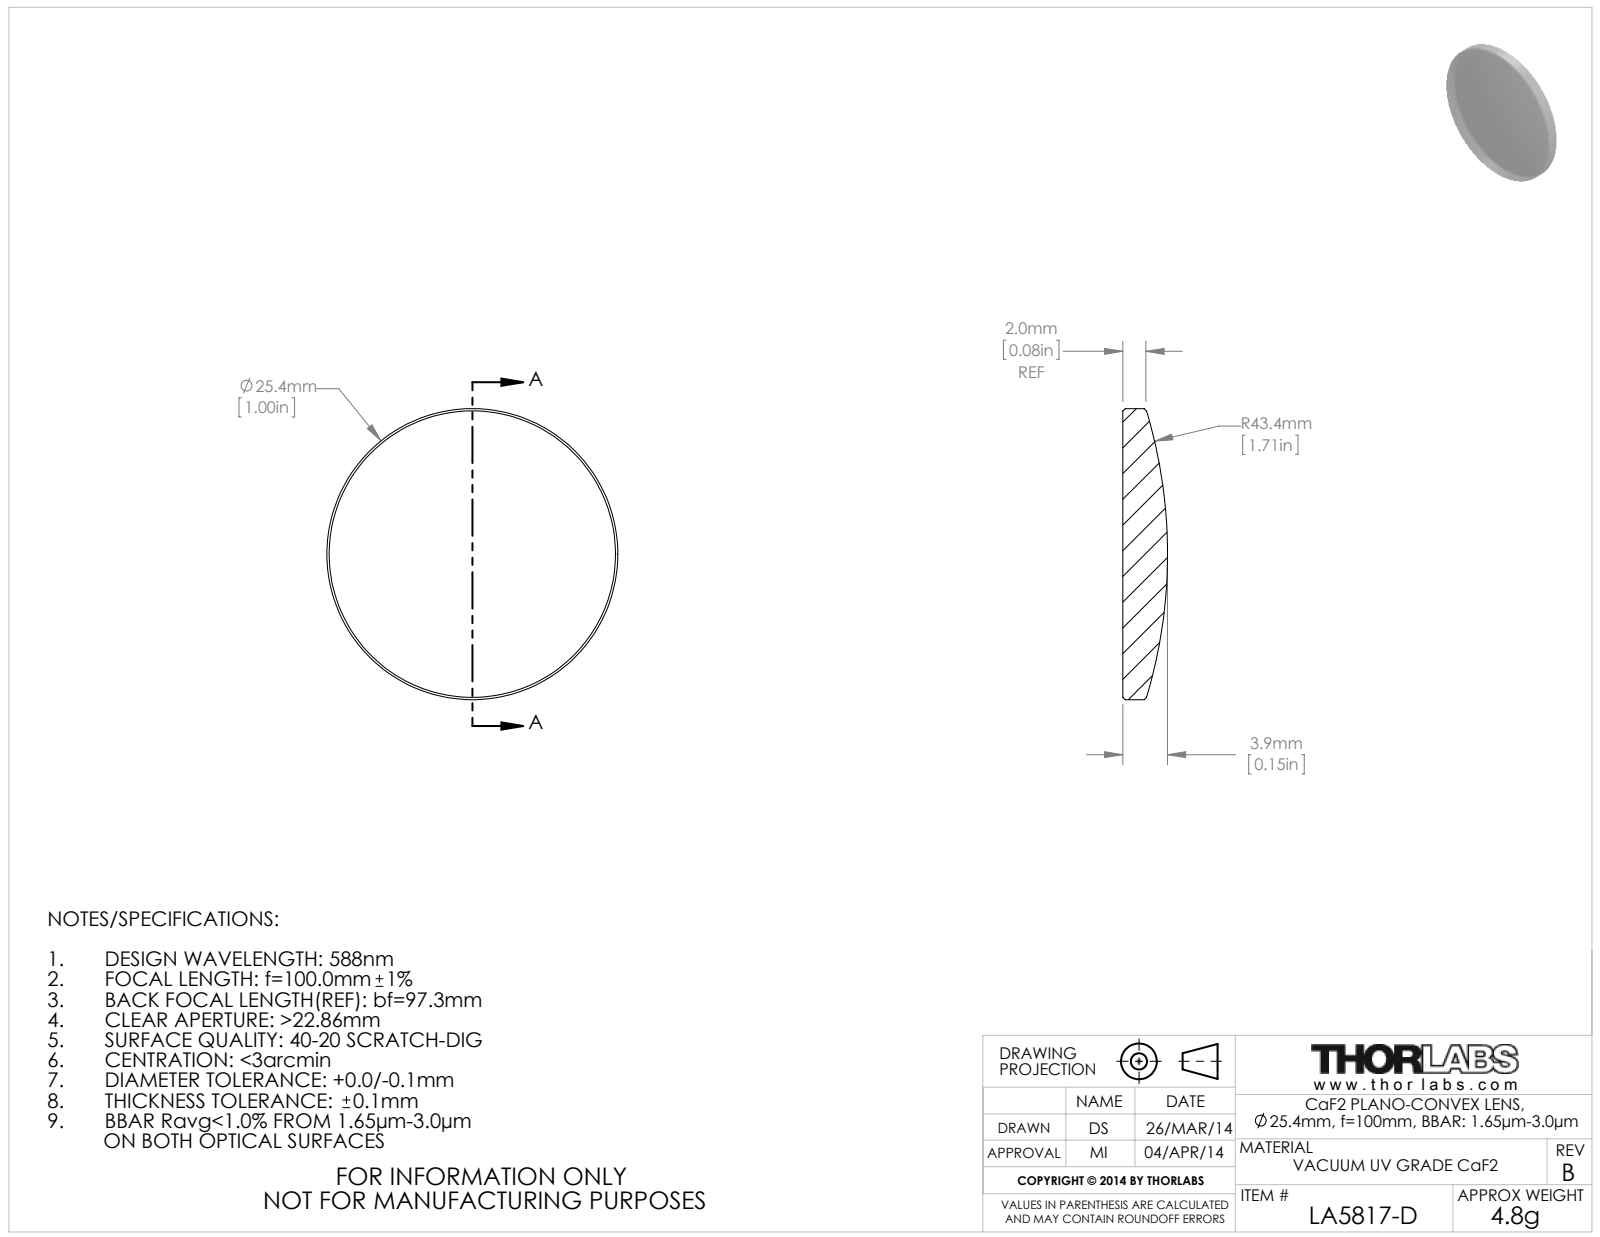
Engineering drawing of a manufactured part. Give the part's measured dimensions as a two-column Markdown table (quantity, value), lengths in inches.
| quantity | value |
| --- | --- |
| part name | 22962-E0W |
| STEP written by | SolidWorks 2011 (AUTOMOTIVE_DESIGN) |
| units | inches |
| bodies | 0 solids, 5 faces (1 planar, 2 cylindrical, 2 other) |
| overall size | 1 × 1 × 0.154 |
| round bosses / shafts (diameter × count) | 1 × 1 |
